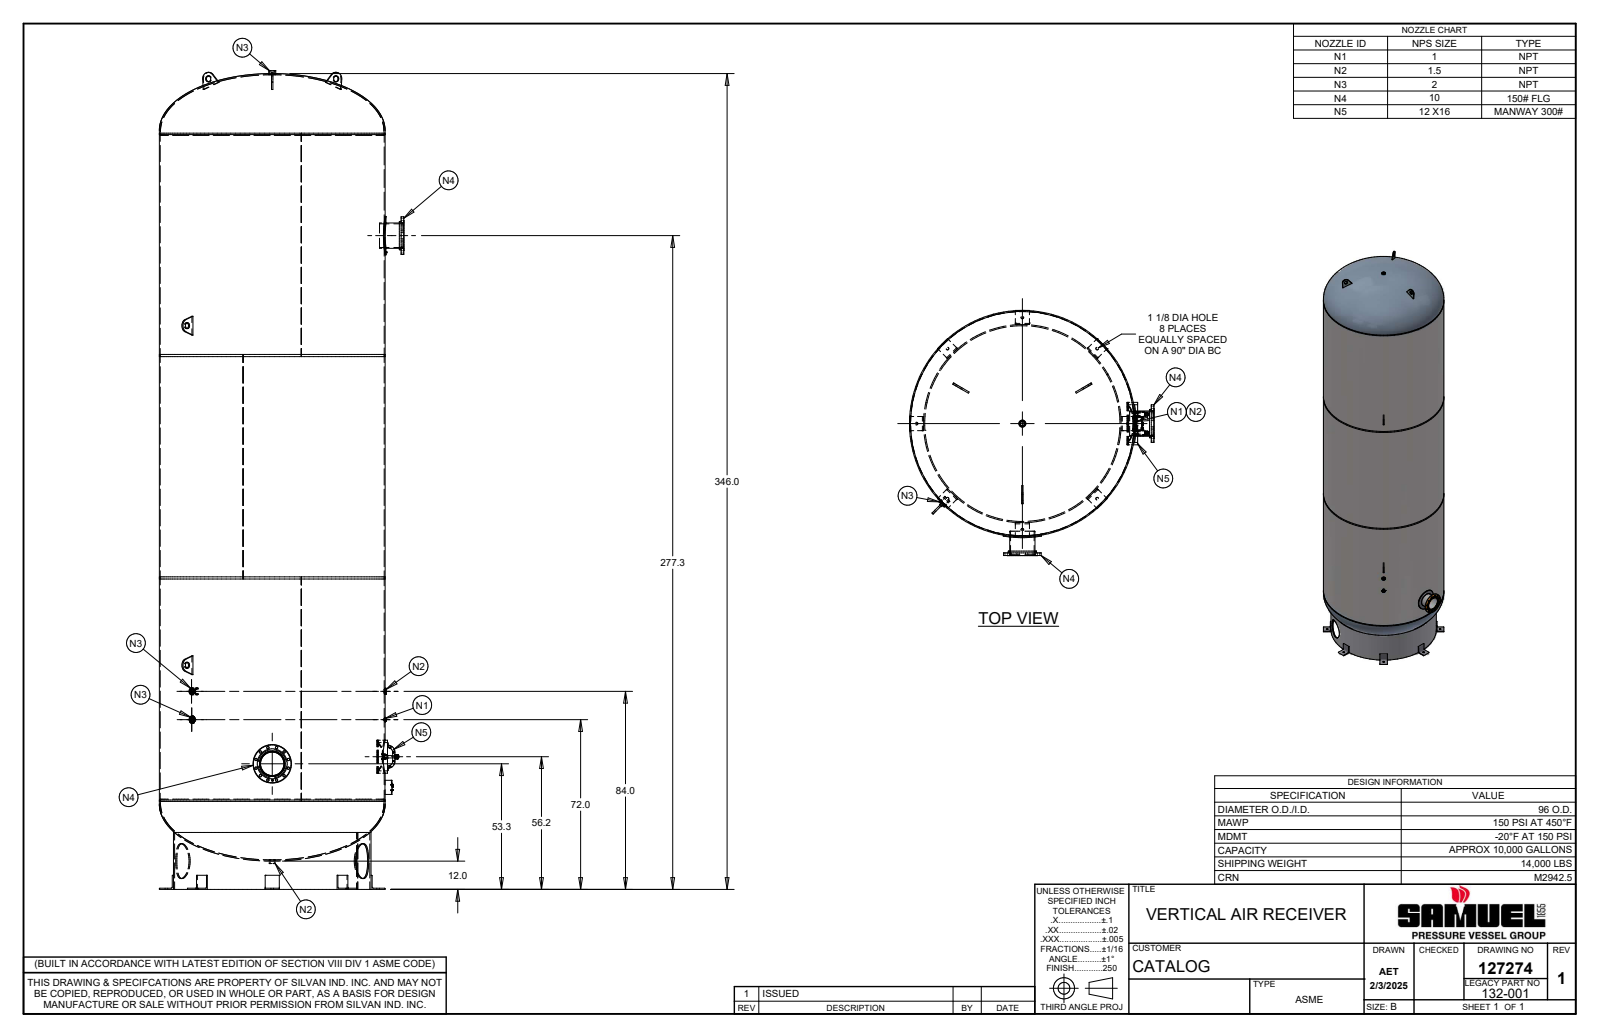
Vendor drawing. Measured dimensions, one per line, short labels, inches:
name: 127274; 127282; 127280; 127281 (+8 more)
written by: Autodesk Inventor 2022 (AUTOMOTIVE_DESIGN)
unit: in
bodies: 48 solids, 1230 faces (661 planar, 223 cylindrical, 346 other)
size: 347.188 × 104 × 104
volume: 46 842 in³; area: 232 146 in²
holes: 25× ⌀1, 10× ⌀1.125, 8× ⌀0.195, 5× ⌀2.5, 4× ⌀0.375, 2× ⌀0.438, 2× ⌀0.865, 2× ⌀2, 2× ⌀2.172, 2× ⌀10, 2× ⌀10.02, 2× ⌀10.813
bosses: 4× ⌀0.469, 4× ⌀0.19, 3× ⌀3, 2× ⌀16.313, 2× ⌀16, 2× ⌀12.75, 2× ⌀12, 2× ⌀10.75
rounds: 16× R0.24, 12× R0.776, 10× R0.375, 8× R0.5, 6× R1, 5× R2.75, 4× R0.75, 4× R1.156
face distances: 0.5, 0.937, 94.313, 0.625, 188.125, 93.813, 94.312, 188.625, 24.128, 23.628
hole spacings: 7.125, 3.688, 10.076, 12.341, 13.765, 14.25, 3.093, 34.441
